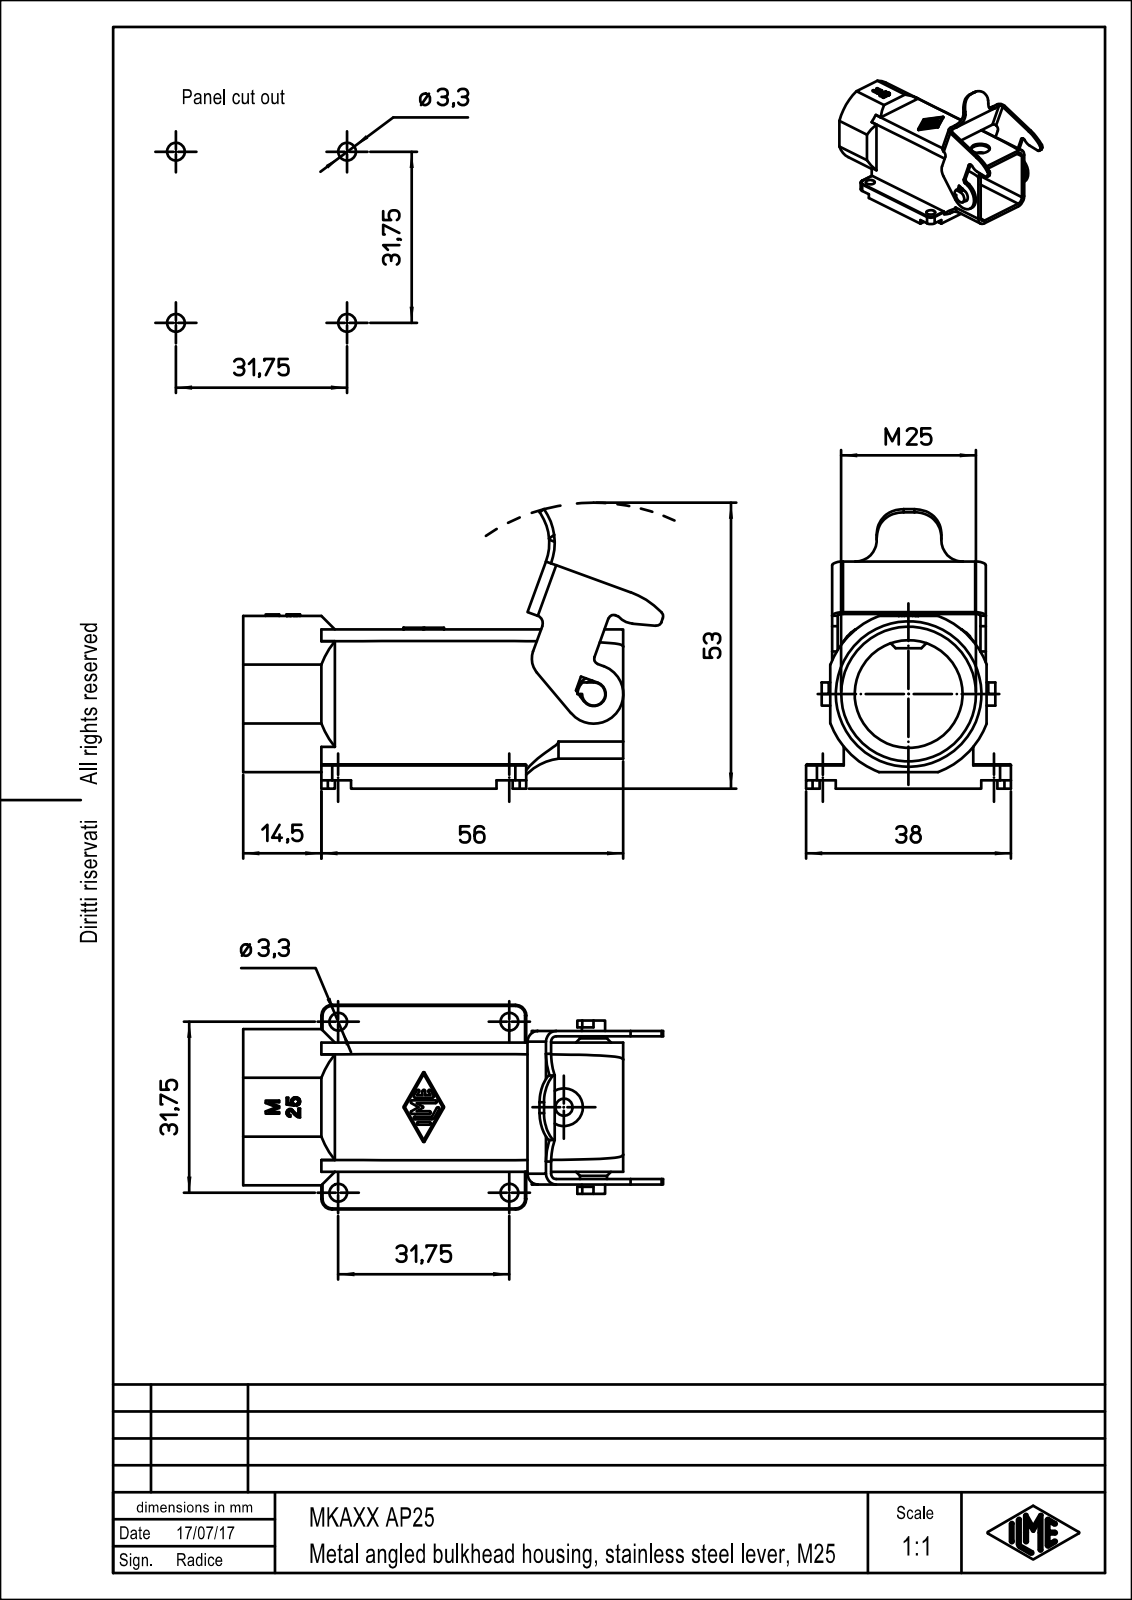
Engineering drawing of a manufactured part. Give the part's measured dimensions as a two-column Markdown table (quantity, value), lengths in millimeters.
| quantity | value |
| --- | --- |
| part name | MKAXX_AP25 |
| STEP written by | PTC Creo Elements/Direct Modeling 19.0E 27-Jun-2016 (C) Parametric Technology GmbH (AUTOMOTIVE_DESIGN) |
| units | millimeters |
| bodies | 1 solid, 387 faces (258 planar, 108 cylindrical, 21 other) |
| overall size | 77.9 × 51.86 × 38 |
| volume | 16 029 mm³ |
| surface area | 18 182 mm² |
| round holes (diameter × count) | 3.3 × 4, 3.2 × 1, 7 × 1, 20 × 1, 25 × 1 |
| round bosses / shafts (diameter × count) | 5 × 1, 4.3 × 1 |
| partial cylindrical surfaces (radius × count) | 2 × 18, 0.25 × 15, 1 × 6, 3.2 × 6, 0.2 × 4, 4 × 4, 0.12 × 3, 5 × 2 |
| main face-to-face distances | 1.2, 22.8, 24, 21.6, 26.5, 1, 2.35, 25.15, 27.5, 2.5 |
| hole center spacings | 31.75, 44.79, 44.9, 18.83, 18.84 |
